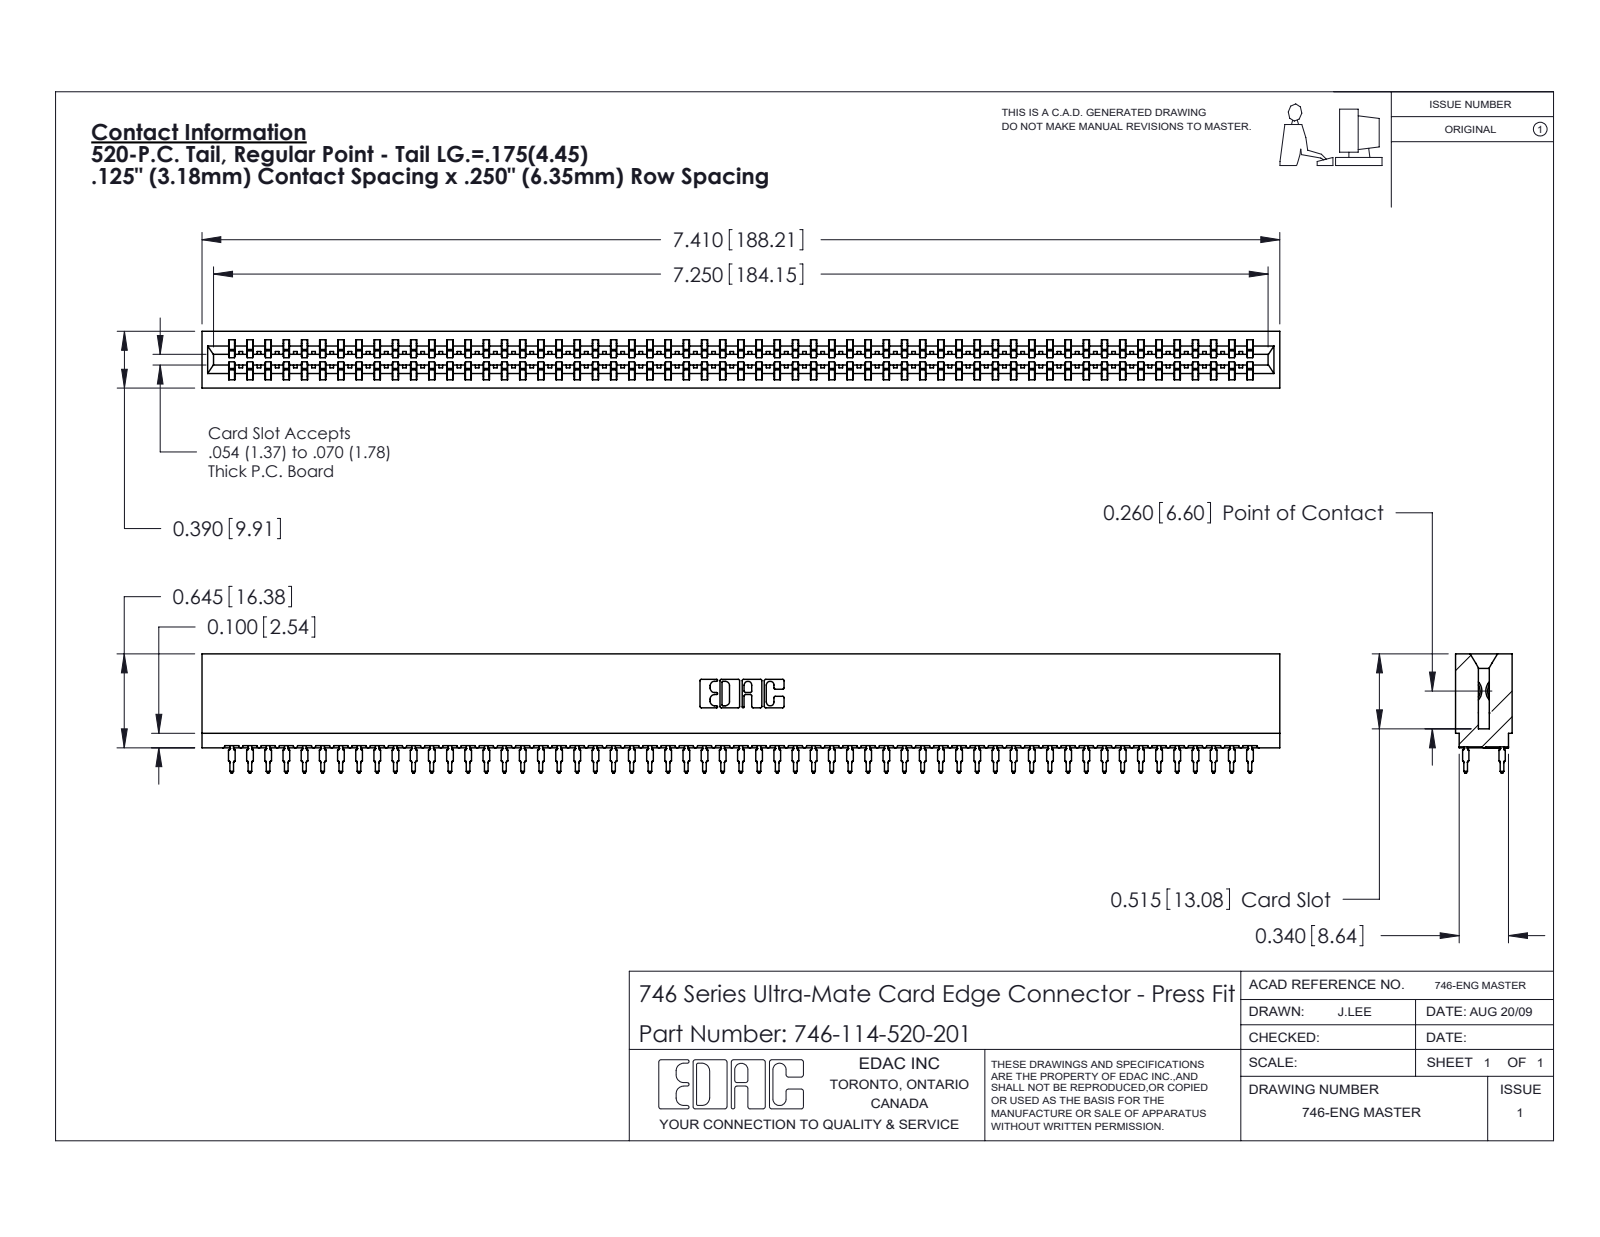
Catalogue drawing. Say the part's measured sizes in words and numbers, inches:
The part is named "746-292-001_520; 746-114-520-201; 746 Part_.515 Slot Depth - 01". Its 3-D file was written by "SolidWorks 2020 (CONFIG_CONTROL_DESIGN)". It is 115 solids with 10300 faces: 5299 planar, 2037 cylindrical and 2964 other. Overall it measures 7.41 by 0.819 by 0.39 inches. Its volume is 1.219 cubic inches and its surface area 49.39 square inches. Partial cylindrical surfaces (rounded edges, fillets, slot ends): 228 of radius 0.021, 58 of radius 0.015, 22 of radius 0.01, 8 of radius 0.005, 8 of radius 0.011, 6 of radius 0.007, 6 of radius 0.031, 3 of radius 0.026. The main face-to-face distances are 0.057, 0.333, 0.39, 0.25, 0.025, 0.307, 0.275, 0.083, 0.174, 0.158.
